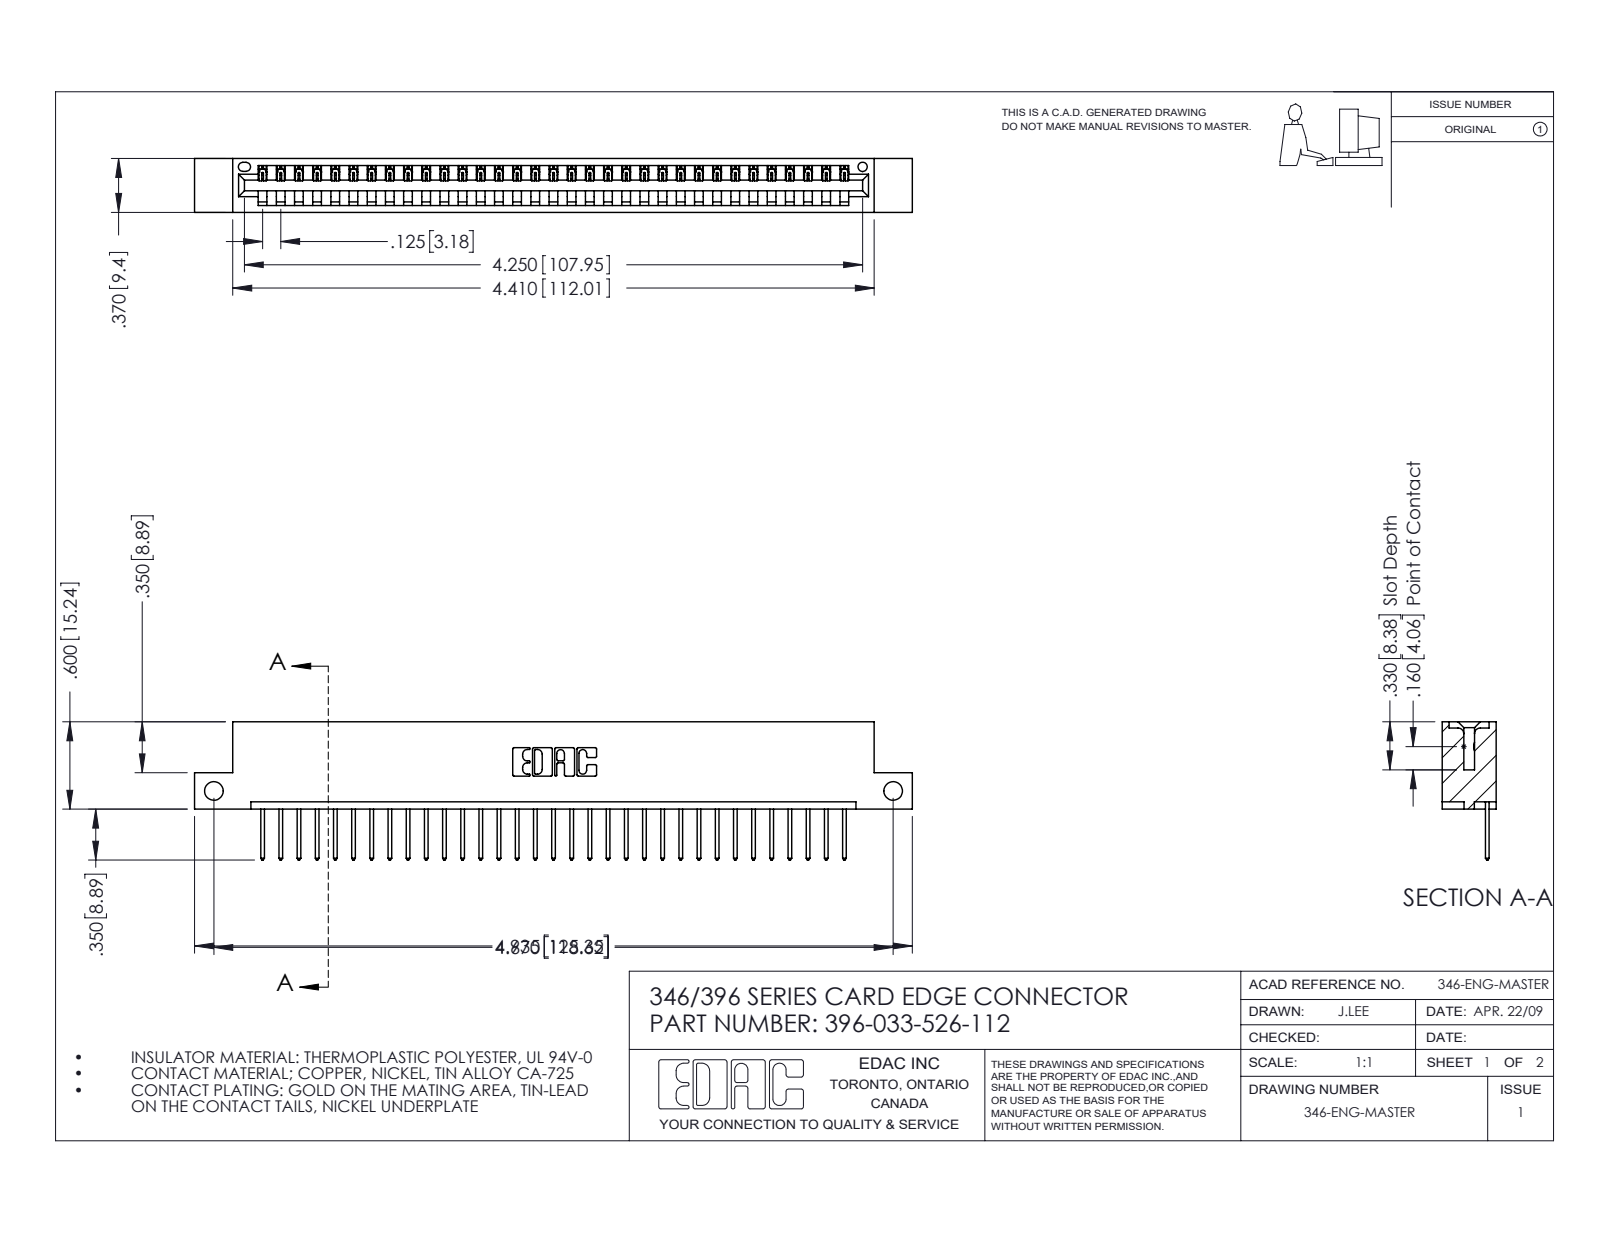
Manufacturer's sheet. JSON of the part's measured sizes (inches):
{"part_name": "345-292-001_345-293-126; 346 Part_Flush Mounting Lugs - Side Mount; 396-033-526-112", "step_written_by": "SolidWorks 2016 (CONFIG_CONTROL_DESIGN)", "units": "inches", "bodies": {"solids": 34, "faces": 2036, "planar": 1396, "cylindrical": 640, "other": 0}, "overall_size": [4.935, 0.95, 0.37], "volume_in3": 0.721, "surface_area_in2": 22.48, "round_holes": [[0.128, 2], [0.064, 1]], "partial_cylinders_radius": [[0.006, 66], [0.01, 66], [0.01, 22], [0.007, 6], [0.031, 6], [0.026, 3], [0.031, 2], [0.04, 2]], "face_to_face_distances": [0.048, 0.322, 0.37, 0.25, 0.072, 0.298, 0.025, 0.148, 0.222, 0.1], "hole_center_spacings": [4.67]}
